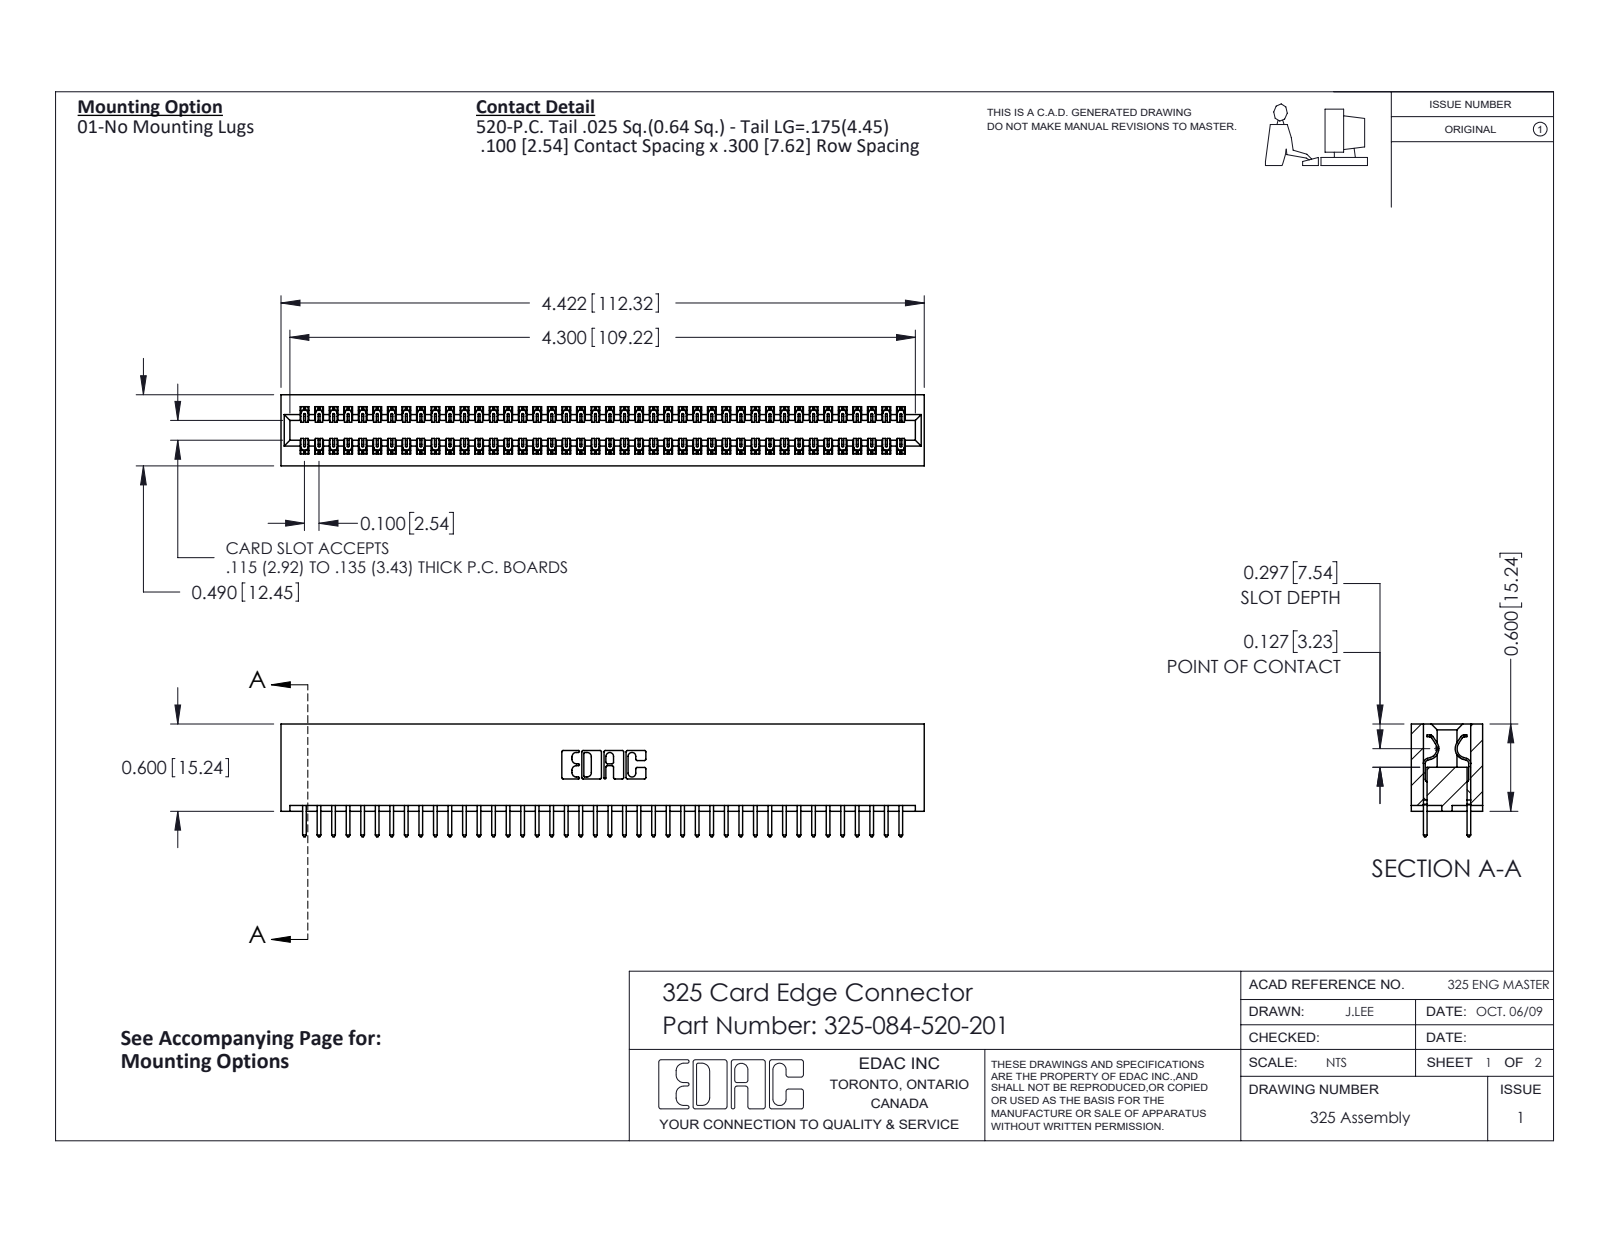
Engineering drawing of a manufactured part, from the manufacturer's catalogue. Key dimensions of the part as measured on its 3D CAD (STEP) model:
Part name (STEP PRODUCT): 325-292-001_325-293-120; 325 Part_Lugless; 325-084-520-201
STEP written by: SolidWorks 2016 (CONFIG_CONTROL_DESIGN)
Units: inches
Bodies: 85 solids, 4474 faces (3090 planar, 1384 cylindrical, 0 other)
Overall size (bounding box): 4.422 × 0.775 × 0.49
Volume: 0.921 in³ · Surface area: 29.08 in²
Partial cylindrical surfaces — rounded edges, fillets, slot ends (radius × count): R0.006 ×126, R0.01 ×84, R0.01 ×22, R0.007 ×6, R0.031 ×6, R0.026 ×3, R0.014 ×2, R0.022 ×2
Main face-to-face distances: 0.083, 0.407, 0.3, 0.49, 0.107, 0.383, 0.025, 0.325, 0.275, 0.56
